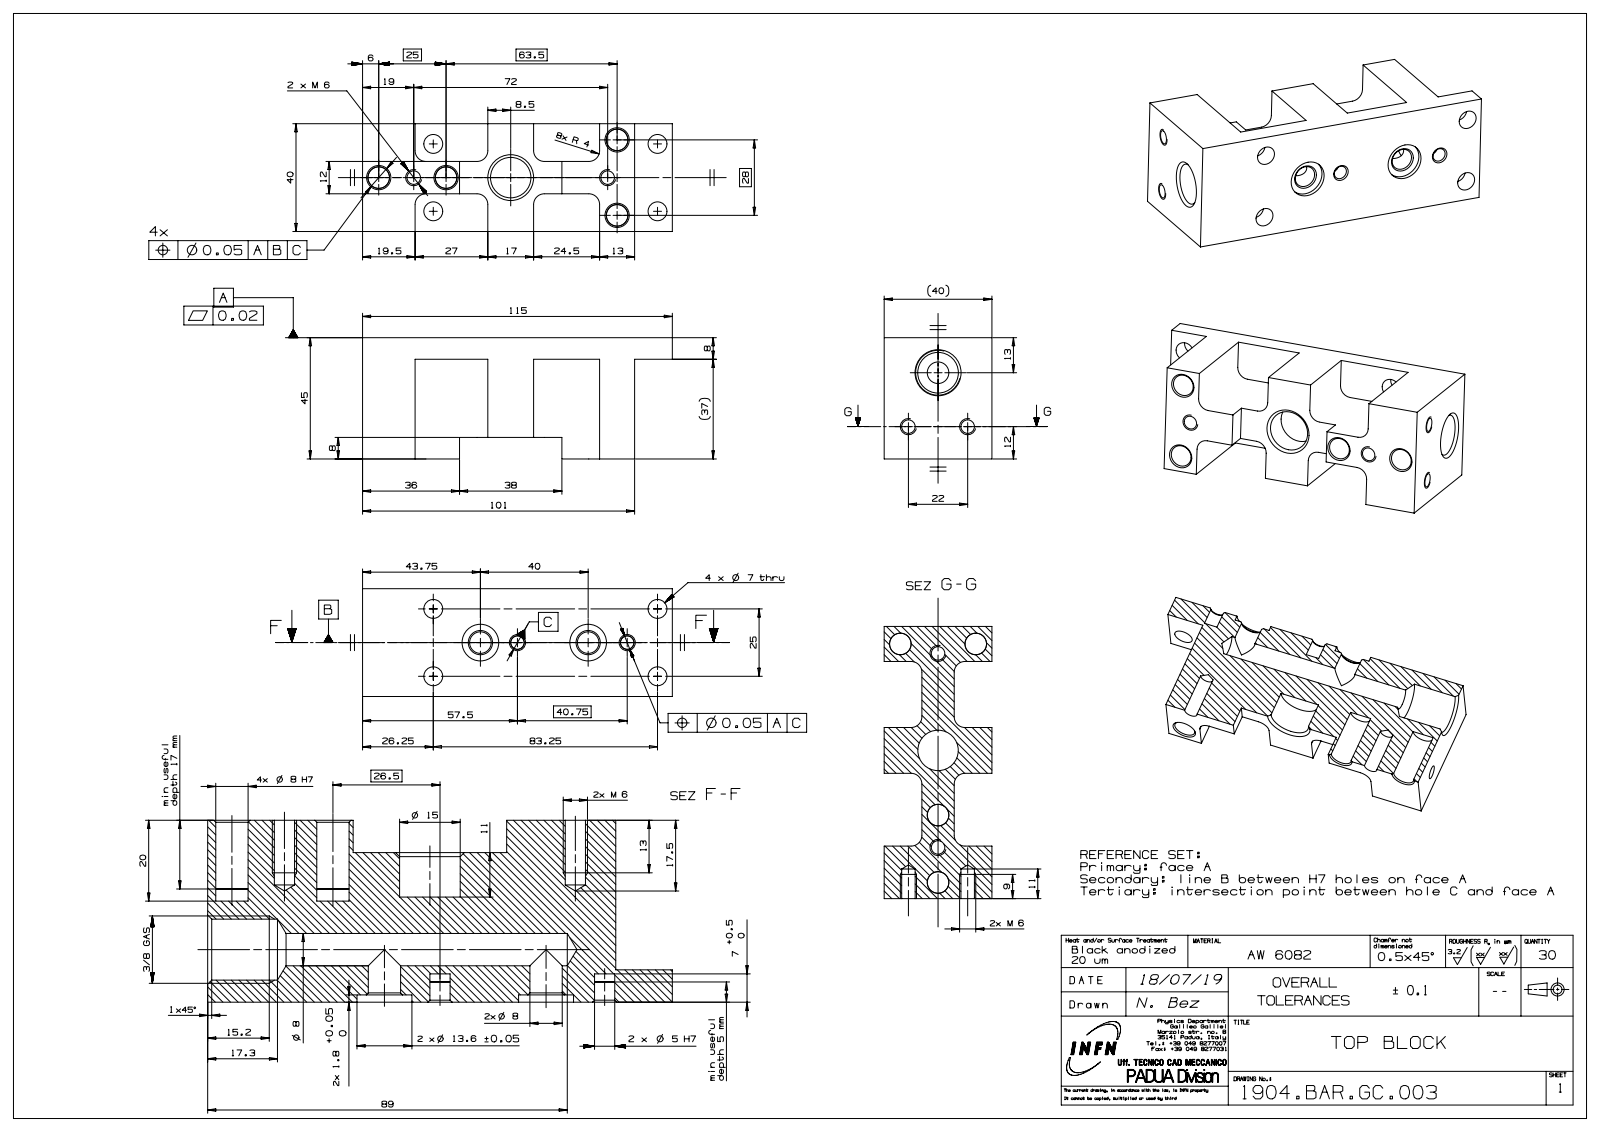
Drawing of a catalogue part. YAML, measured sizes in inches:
part_name: "bmas477C8C18u68b"
step_written_by: "SIEMENS PLM Software NX 12.0 (AUTOMOTIVE_DESIGN)"
units: inches
bodies: {solids: 1, faces: 82, planar: 37, cylindrical: 29, other: 16}
overall_size: [4.528, 1.772, 1.575]
volume: 6.686
surface_area: 49.29
round_holes:
  - {diameter: 0.315, count: 7}
  - {diameter: 0.197, count: 6}
  - {diameter: 0.276, count: 4}
  - {diameter: 0.535, count: 2}
  - {diameter: 0.591, count: 1}
  - {diameter: 0.594, count: 1}
partial_cylinders:
  - {radius: 0.157, count: 8}
face_to_face_distances: [0.551, 1.575, 1.024, 0.315, 1.457, 3.976, 0.472, 1.772, 2.697, 1.063]
hole_center_spacings: [0.984, 0.285, 0.526, 0.568, 0.569, 0.57, 0.593, 0.662]
